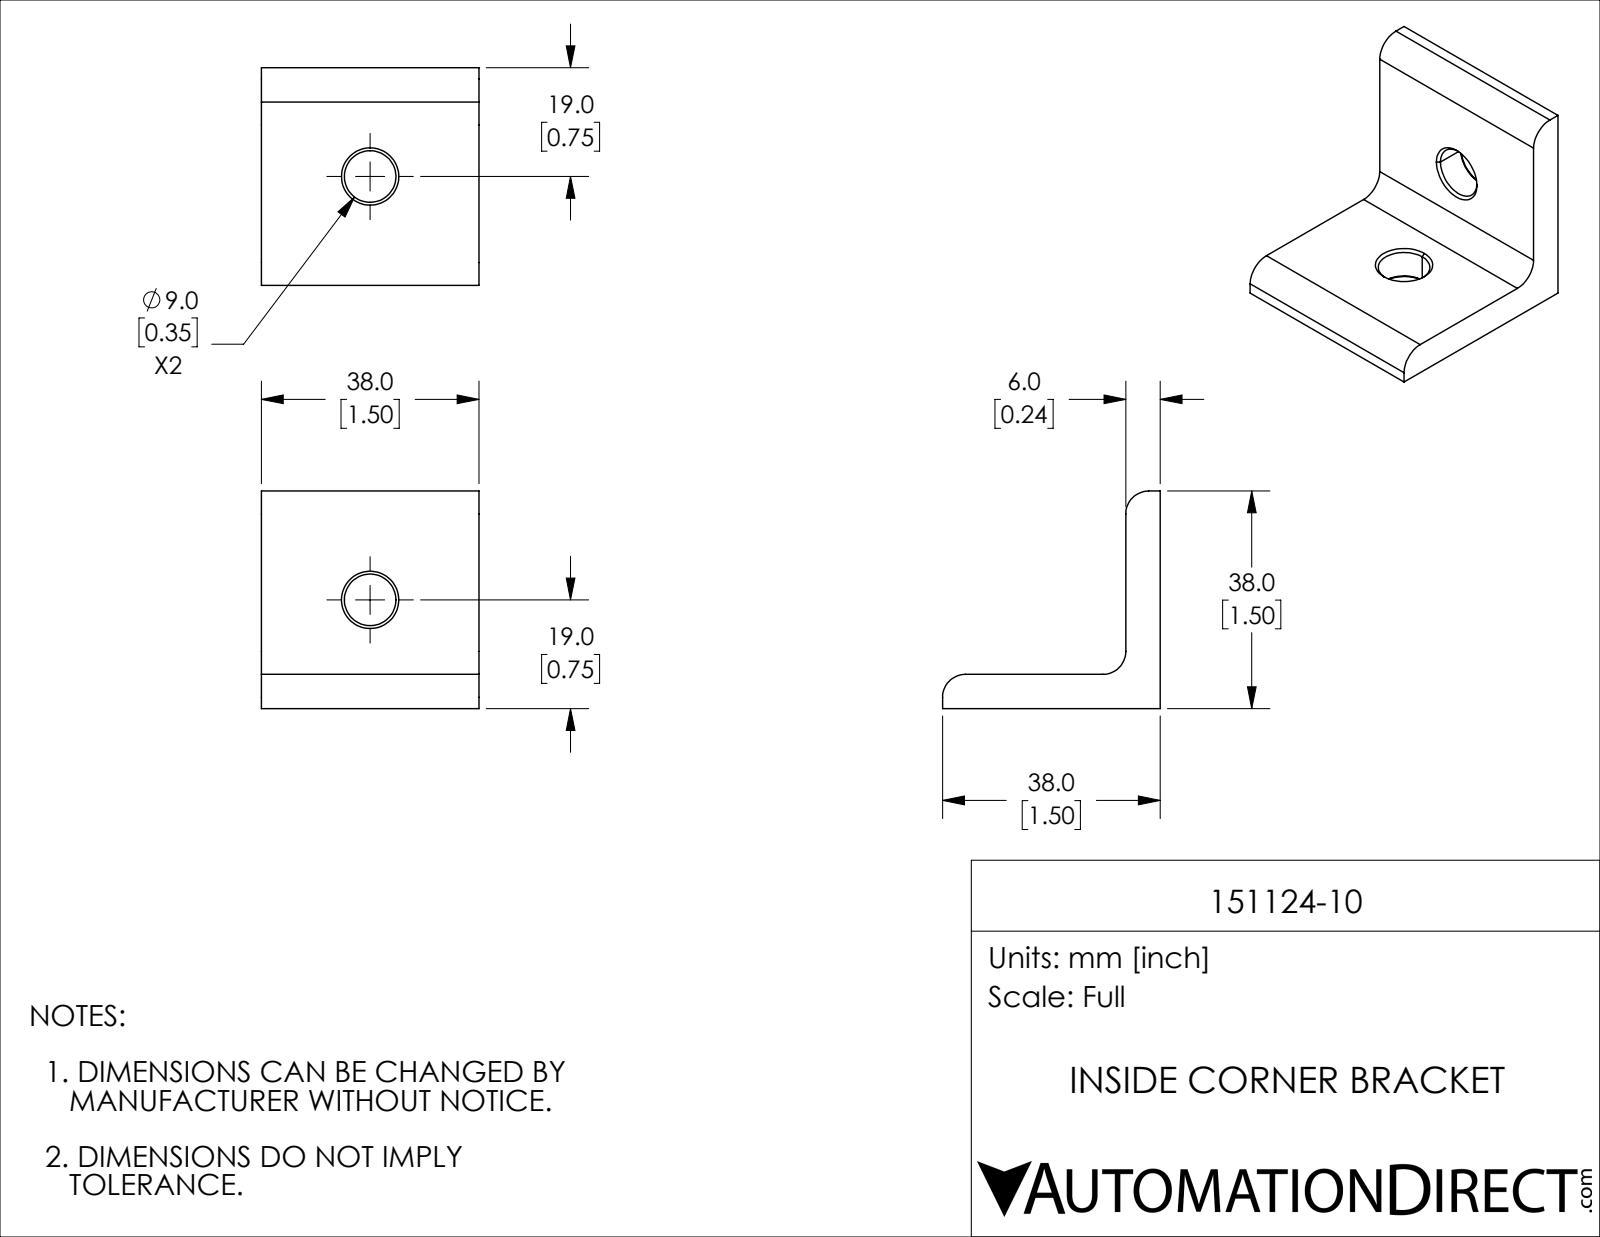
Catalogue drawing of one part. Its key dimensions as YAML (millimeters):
part_name: "151124-10"
step_written_by: "SolidWorks 2024 (CONFIG_CONTROL_DESIGN)"
units: millimeters
bodies: {solids: 1, faces: 23, planar: 8, cylindrical: 7, other: 8}
overall_size: [38, 38, 38]
volume: 15051
surface_area: 6466
round_holes:
  - {diameter: 9, count: 2}
partial_cylinders:
  - {radius: 4, count: 3}
face_to_face_distances: [6, 38, 32]
